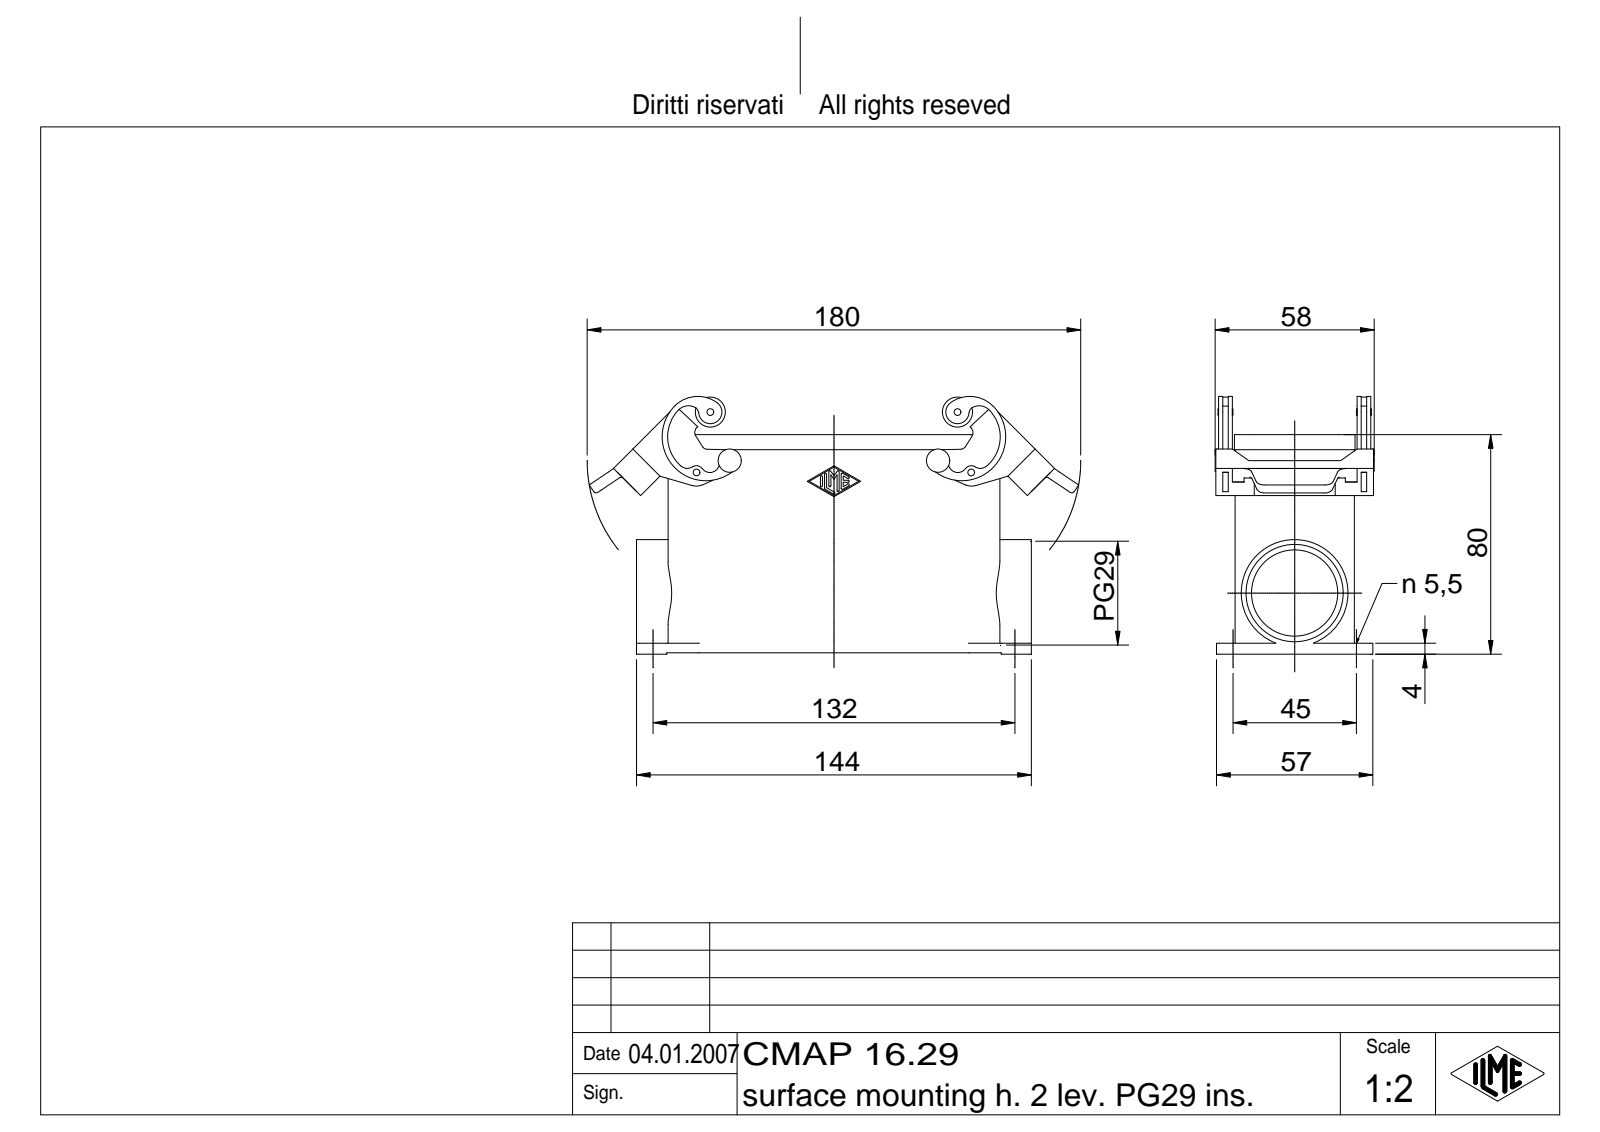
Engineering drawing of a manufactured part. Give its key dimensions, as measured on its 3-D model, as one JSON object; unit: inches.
{"part_name": "CMAP 16.29", "step_written_by": "Autodesk Inventor 7 (AUTOMOTIVE_DESIGN)", "units": "inches", "bodies": {"solids": 1, "faces": 753, "planar": 193, "cylindrical": 207, "other": 353}, "overall_size": [7.027, 3.698, 2.283], "volume_in3": 8.508, "surface_area_in2": 128.4, "round_holes": [[0.079, 4], [0.217, 4], [0.098, 2], [1.239, 1], [1.397, 1]], "round_bosses_or_shafts": [[0.433, 2], [0.197, 2], [0.118, 2], [1.535, 1]], "partial_cylinders_radius": [[0.039, 20], [0.015, 14], [0.118, 12], [0.236, 8], [0.098, 6], [0.059, 4], [0.079, 4], [0.138, 4]], "face_to_face_distances": [0.118, 1.594, 1.713, 1.476, 0.138, 0.157, 0.03, 1.988, 1.604, 0.148], "hole_center_spacings": [0.888, 1.772, 3.845, 5.197, 5.491, 3.549, 3.944]}
